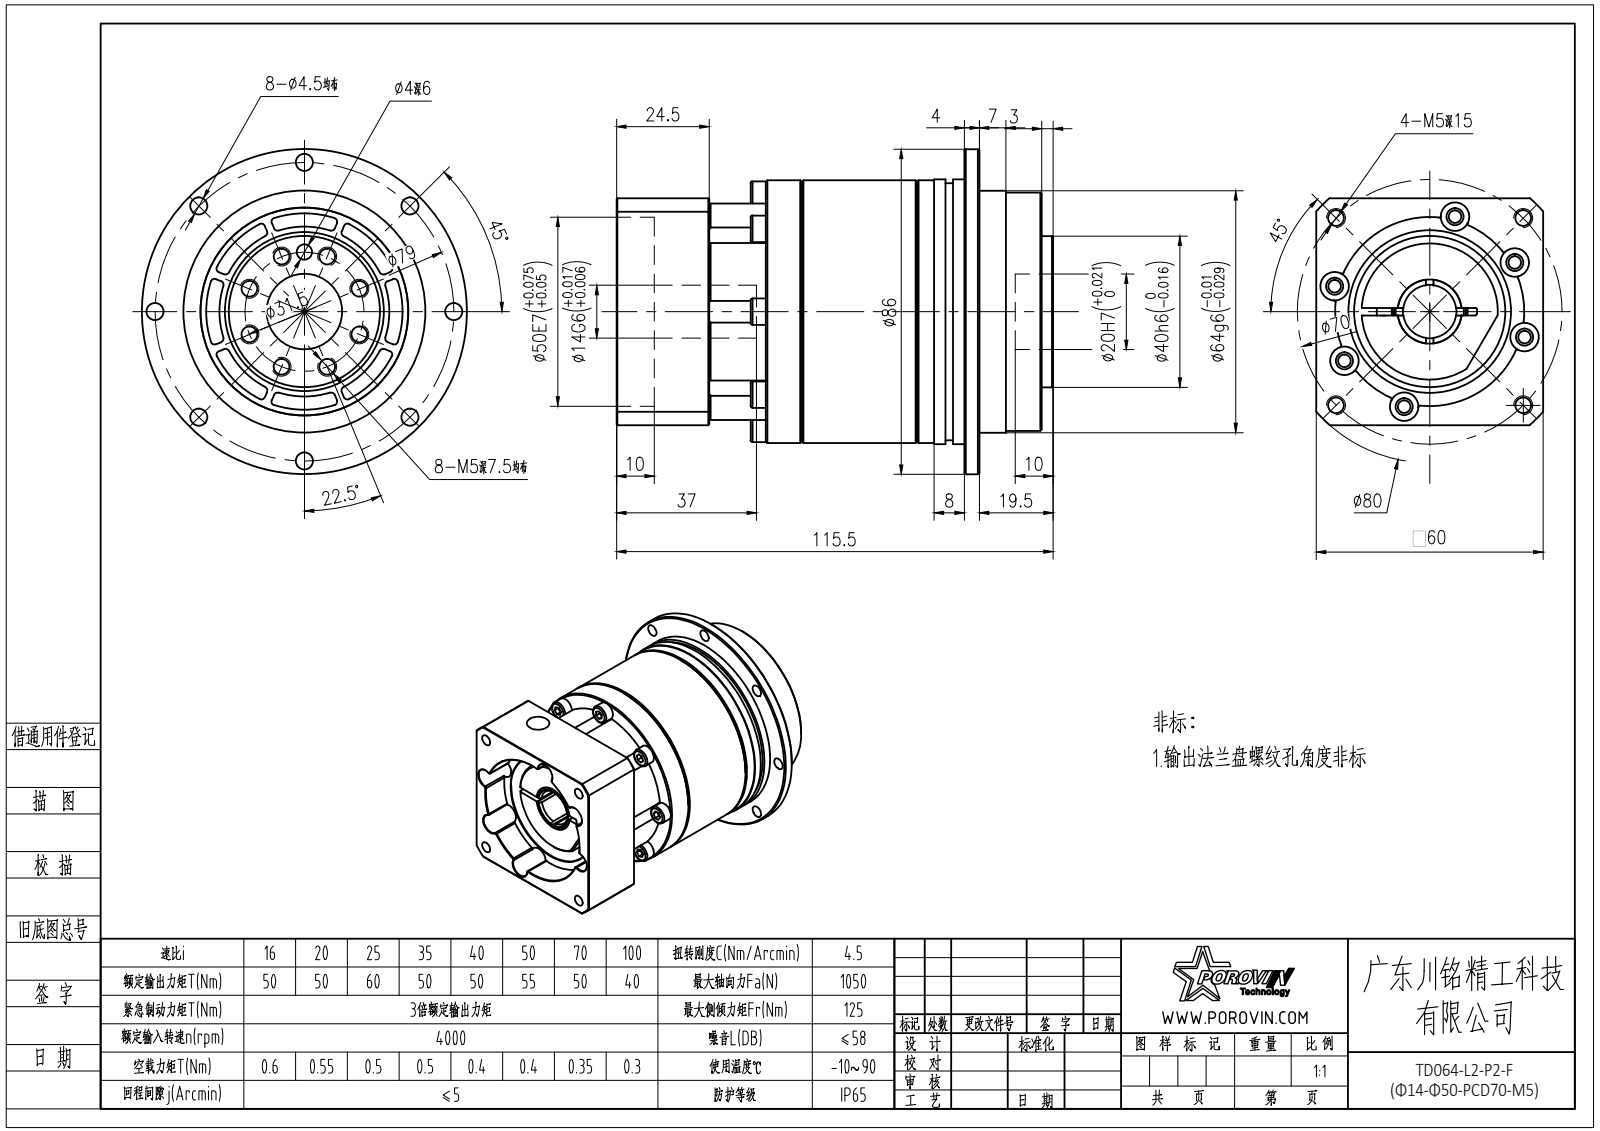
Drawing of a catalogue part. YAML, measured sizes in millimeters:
part_name: "二级齿圈KD64外形图; hex socket set screws with flat point gb_GB_FASTENER_SCREWS_HSFP M10X10-N; hexagon socket head cap screws gb_GB_FASTENER_SCREWS_HSHCS M5X16-N; hexagon socket head cap screws gb_GB_FASTENER_SCREWS_HSHCS M4X20-N (+2 more)"
step_written_by: "SolidWorks 2016 (CONFIG_CONTROL_DESIGN)"
units: millimeters
bodies: {solids: 36, faces: 1074, planar: 409, cylindrical: 423, other: 242}
overall_size: [115.5, 86, 86]
volume: 269161
surface_area: 83808
round_holes:
  - {diameter: 4.5, count: 22}
  - {diameter: 4.4, count: 14}
  - {diameter: 4.2, count: 12}
  - {diameter: 6, count: 7}
  - {diameter: 3.3, count: 6}
  - {diameter: 7.5, count: 6}
  - {diameter: 5, count: 1}
  - {diameter: 5.5, count: 1}
  - {diameter: 8.5, count: 1}
  - {diameter: 14, count: 1}
  - {diameter: 14.2, count: 1}
  - {diameter: 20, count: 1}
round_bosses_or_shafts:
  - {diameter: 7, count: 14}
  - {diameter: 6.6, count: 14}
  - {diameter: 4, count: 14}
  - {diameter: 86, count: 1}
  - {diameter: 70, count: 1}
  - {diameter: 69.5, count: 1}
  - {diameter: 68, count: 1}
  - {diameter: 64, count: 1}
partial_cylinders:
  - {radius: 1, count: 32}
  - {radius: 0.5, count: 12}
  - {radius: 3.75, count: 8}
  - {radius: 4.75, count: 1}
  - {radius: 22.5, count: 1}
  - {radius: 28.75, count: 1}
  - {radius: 40, count: 1}
face_to_face_distances: [60, 16.5, 24.5, 30.5, 55, 71.5, 47, 5, 11.5, 7.5]
hole_center_spacings: [34.77, 30.47, 42.52, 51.85, 22.77, 28.1, 50.21, 65.21]
